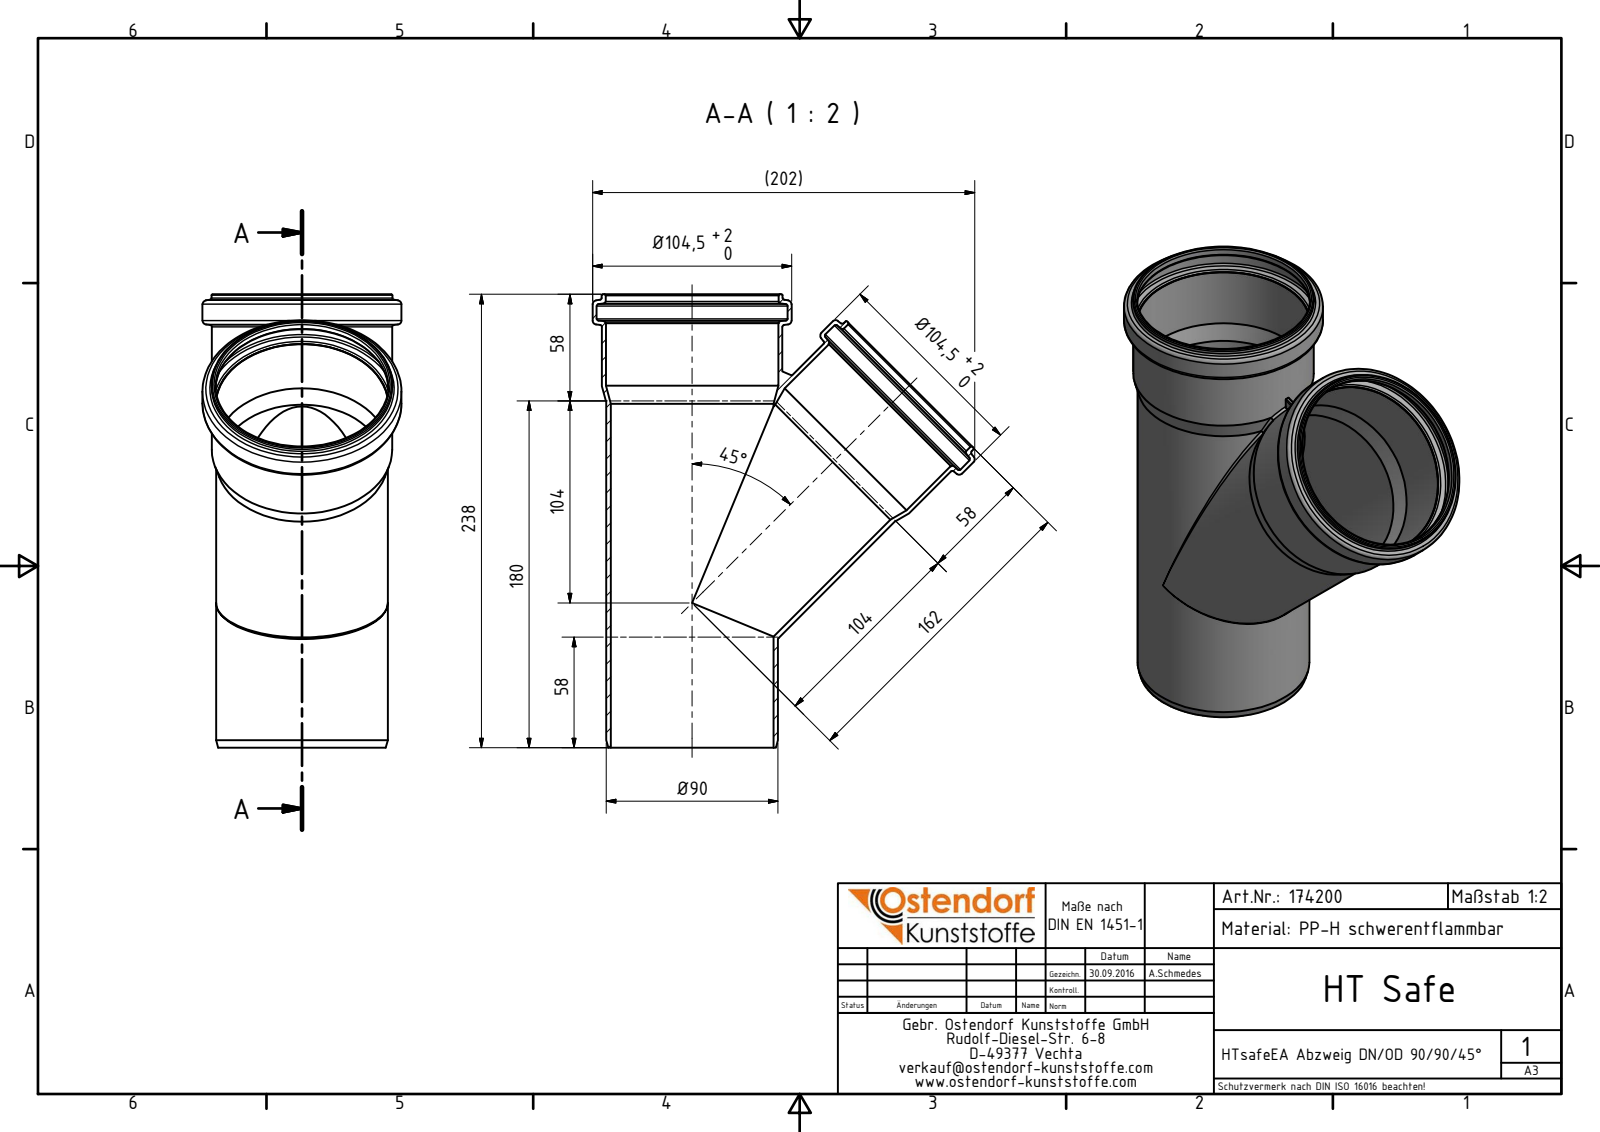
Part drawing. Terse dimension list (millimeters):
name: 174200 HTsafeEA DN_OD 90_90_45°
written by: Autodesk Inventor 2016 (AUTOMOTIVE_DESIGN)
unit: mm
bodies: 1 solid, 68 faces (8 planar, 20 cylindrical, 40 other)
size: 238 × 200.65 × 104.5
volume: 217 902 mm³; area: 191 391 mm²
holes: 3× ⌀90.8, 2× ⌀85.4, 2× ⌀90.5, 2× ⌀100.3
bosses: 2× ⌀104.5, 2× ⌀95, 2× ⌀94.7, 2× ⌀90.2
rounds: 2× R0.5
face distances: 238, 15.21, 222.79, 2.4
